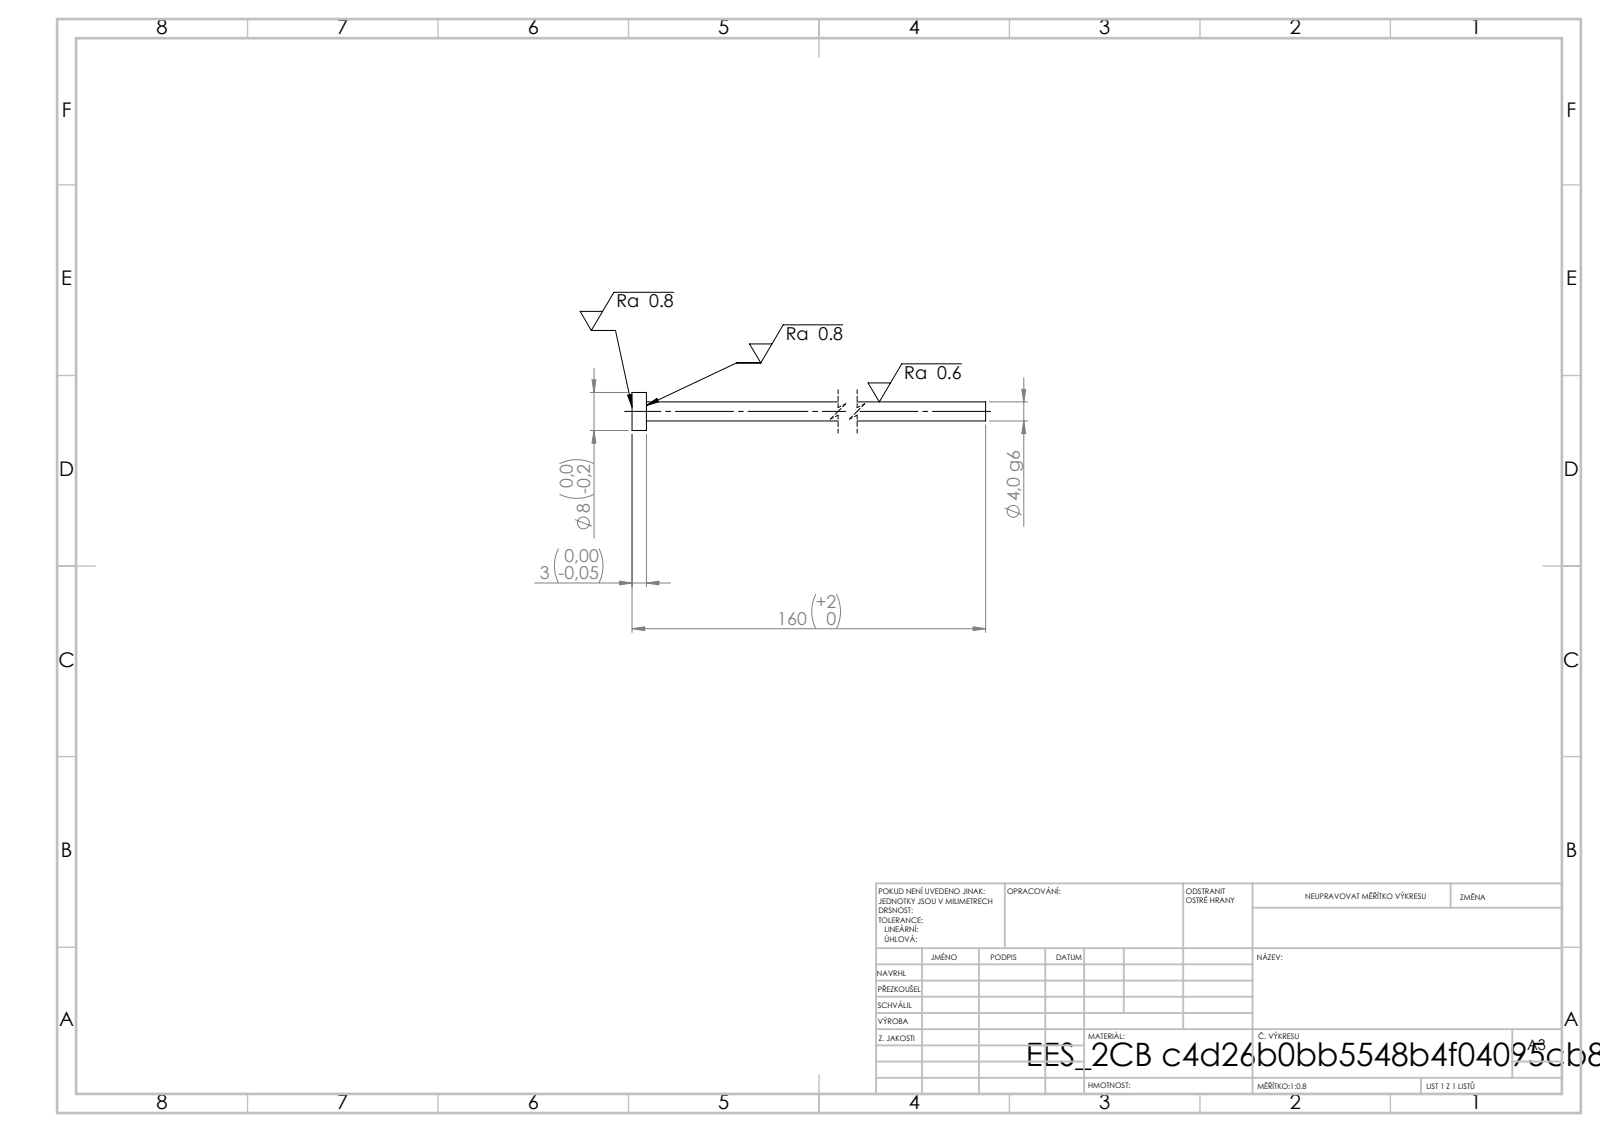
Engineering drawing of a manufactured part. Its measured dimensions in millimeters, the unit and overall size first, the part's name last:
Units: millimetres
Overall size (bounding box): 160 × 8 × 8
Round bosses / shafts (diameter × count): ⌀8 ×1, ⌀4 ×1
Main face-to-face distances: 3, 160, 157
Volume: 2 124 mm³ · Surface area: 2 149 mm²
Bodies: 1 solid, 7 faces (3 planar, 4 cylindrical, 0 other)
STEP written by: SolidWorks 2019 (CONFIG_CONTROL_DESIGN)
